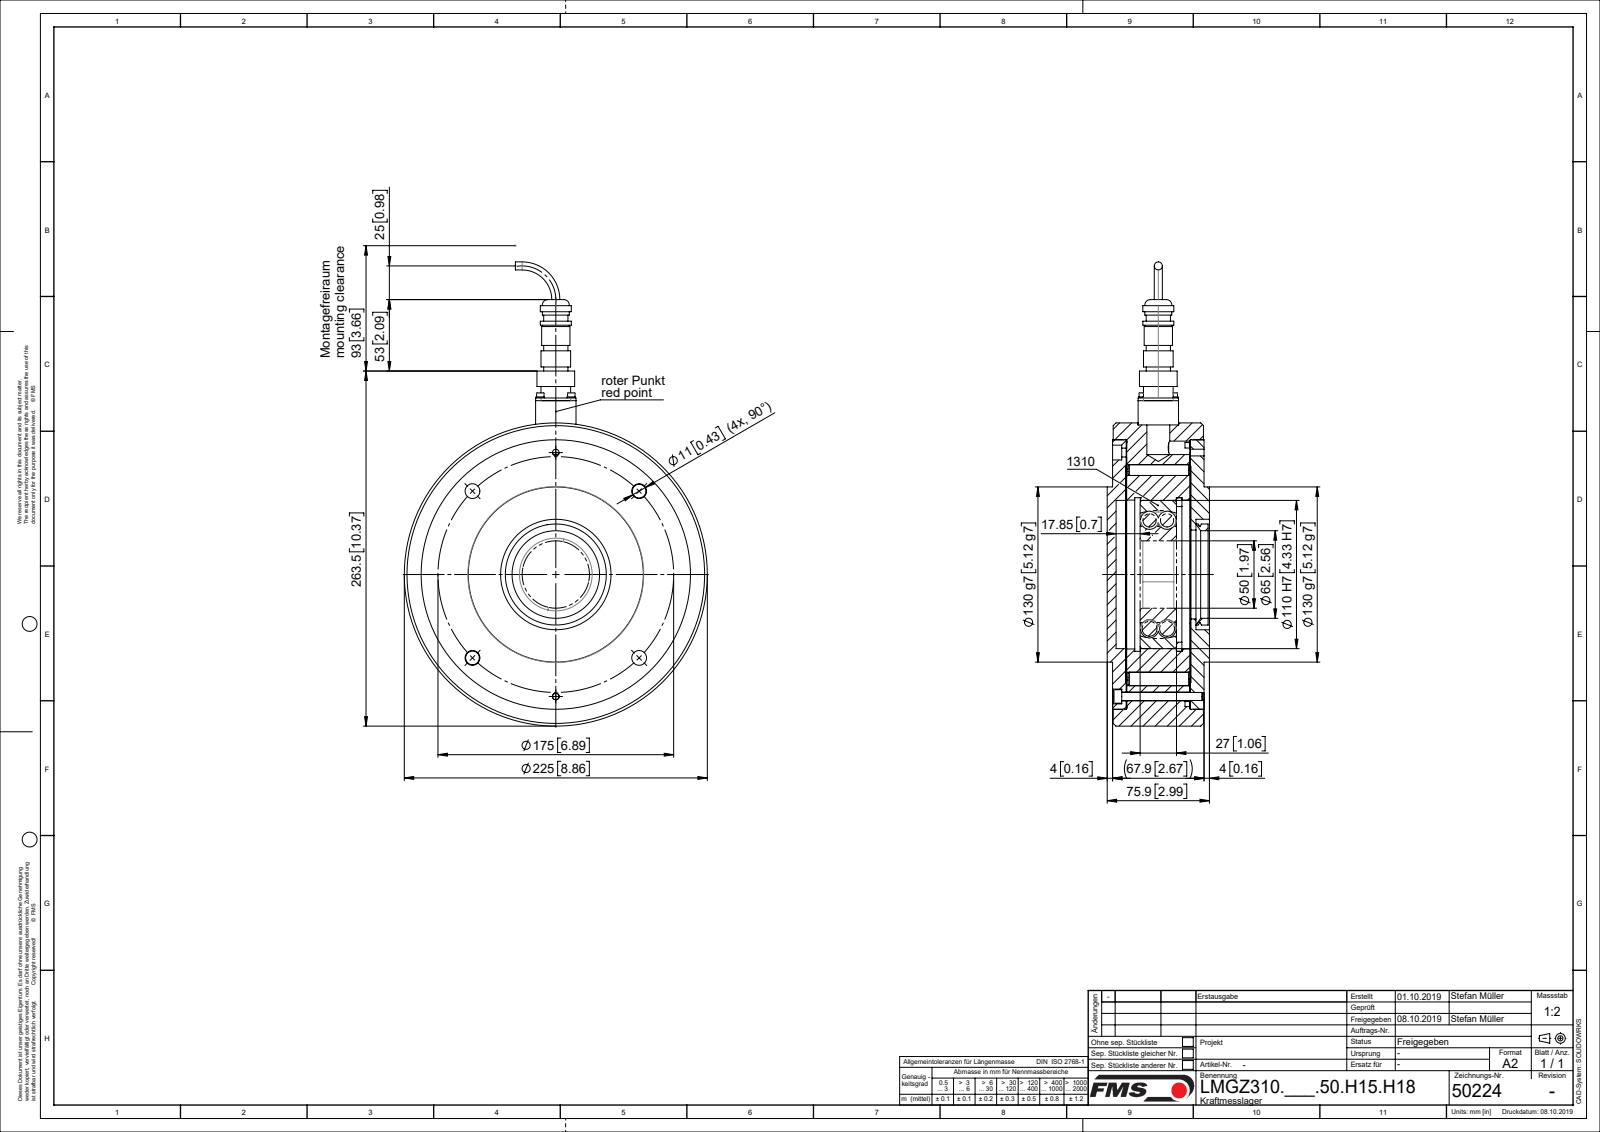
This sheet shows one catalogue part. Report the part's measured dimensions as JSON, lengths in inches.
{"part_name": "ZEICHNUNG7; L50224; L49152; TEIL1 (+8 more)", "step_written_by": "Mechanical Desktop 2007 (CONFIG_CONTROL_DESIGN)", "units": "inches", "bodies": {"solids": 19, "faces": 374, "planar": 96, "cylindrical": 226, "other": 52}, "overall_size": [13.563, 8.858, 2.988], "volume_in3": 147.2, "surface_area_in2": 604, "round_holes": [[0.433, 6], [0.102, 4], [0.126, 4], [0.134, 4], [0.354, 4], [0.197, 2], [0.26, 2], [1.969, 1], [2.52, 1], [2.598, 1], [3.228, 1], [3.472, 1]], "round_bosses_or_shafts": [[0.244, 4], [0.217, 4], [0.118, 4], [0.098, 4], [0.236, 2], [8.858, 1], [7.835, 1], [5.118, 1]], "partial_cylinders_radius": [[0.157, 4], [3.189, 1], [3.386, 1]], "face_to_face_distances": [0.382, 1.86, 0.411, 0.423, 1.868, 2.272, 0.402, 2.262, 1.85, 0.394], "hole_center_spacings": [0.906, 3.445, 1.281, 2.684, 2.684, 3.563, 4.872, 4.872]}
